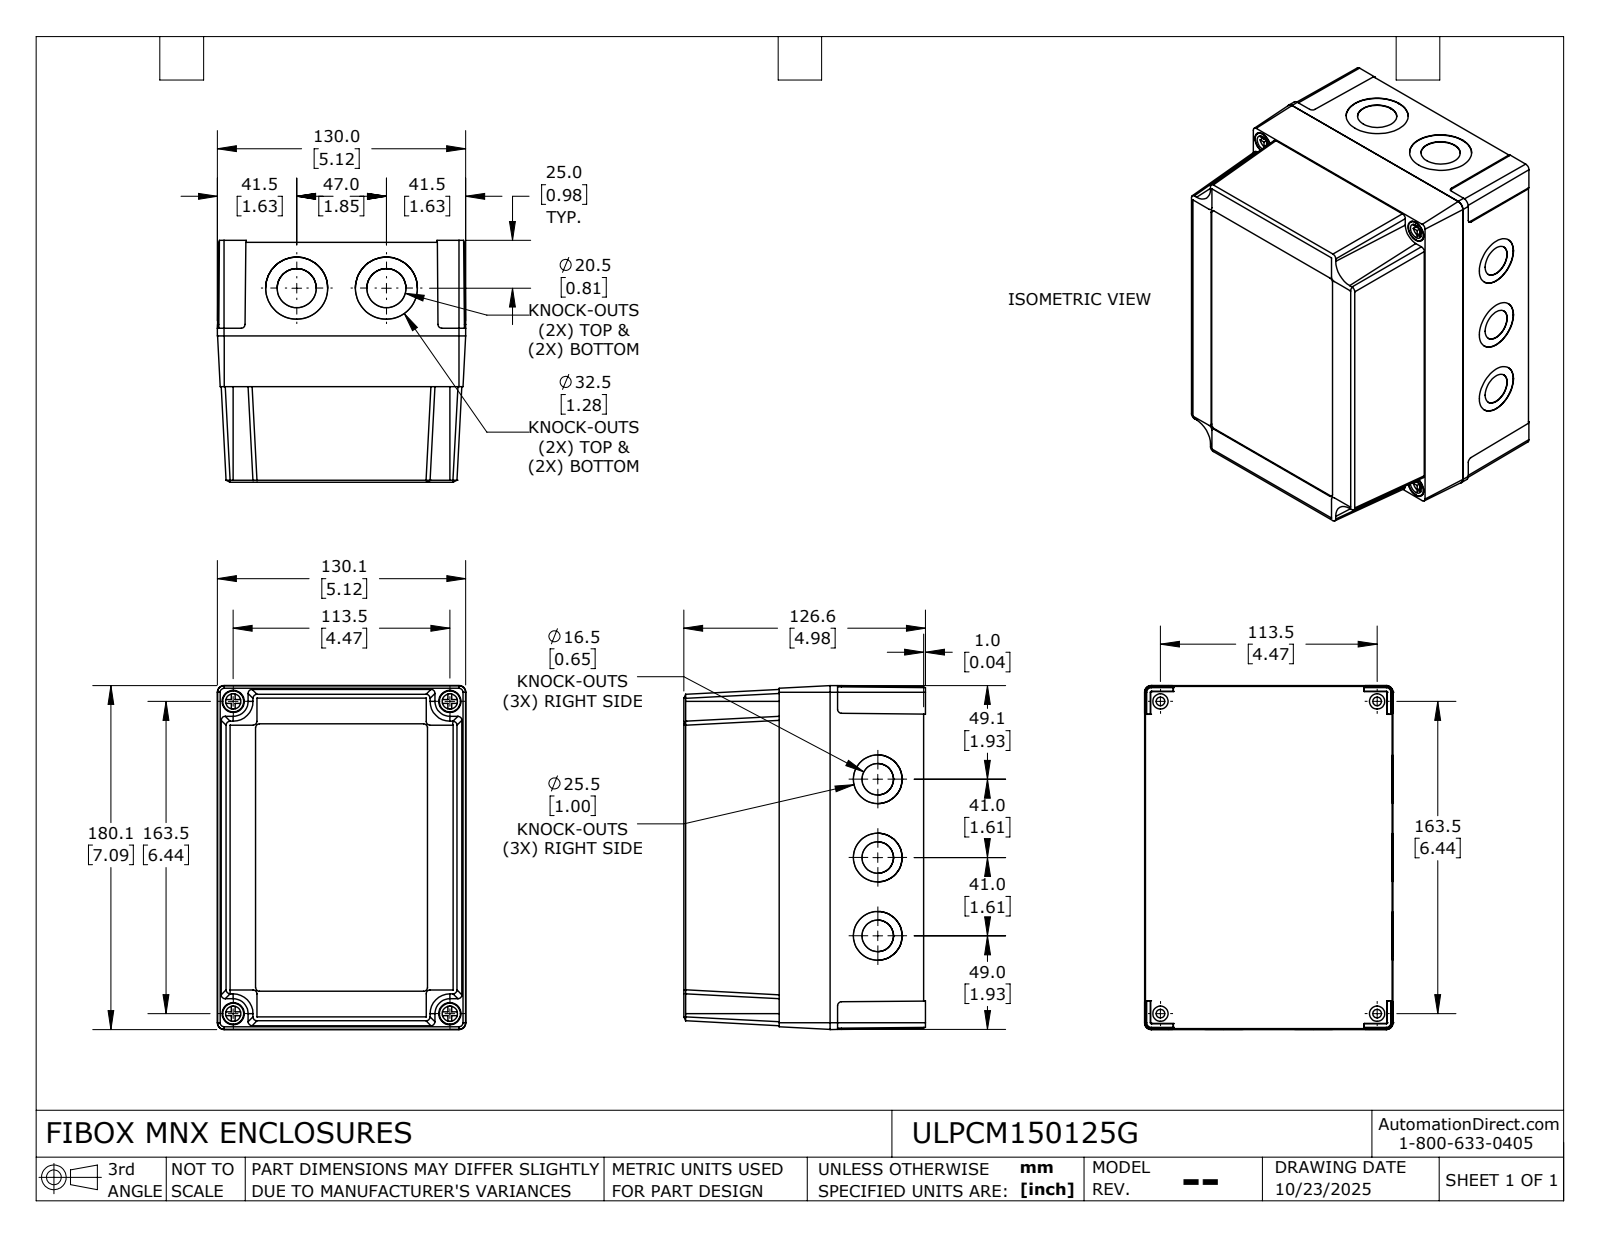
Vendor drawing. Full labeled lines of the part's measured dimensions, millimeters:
Part name (STEP PRODUCT): ULPCM150125G_Default
STEP written by: SolidWorks 2024 (CONFIG_CONTROL_DESIGN)
Units: millimetres
Bodies: 6 solids, 581 faces (335 planar, 200 cylindrical, 46 other)
Overall size (bounding box): 180.1 × 130.1 × 126.6
Volume: 359 200 mm³ · Surface area: 248 800 mm²
Round holes (diameter × count): ⌀3.2 ×8, ⌀4 ×8, ⌀16.5 ×6, ⌀25.5 ×6, ⌀4.5 ×4, ⌀8 ×4, ⌀11.6 ×4, ⌀20.5 ×4, ⌀32.5 ×4
Round bosses / shafts (diameter × count): ⌀8 ×8, ⌀2.5 ×8, ⌀11 ×4, ⌀7.2 ×4
Partial cylindrical surfaces — rounded edges, fillets, slot ends (radius × count): R2 ×8, R2.1 ×8, R1.4 ×6, R0.5 ×4, R5 ×4, R0.6 ×2
Main face-to-face distances: 1.4, 3, 122.7, 119.7, 4.2, 125.1, 122.1, 2.4, 2, 0.6
Hole centre spacings: 33.9, 41, 49.3, 50, 57.9, 82.6, 83.2, 103
